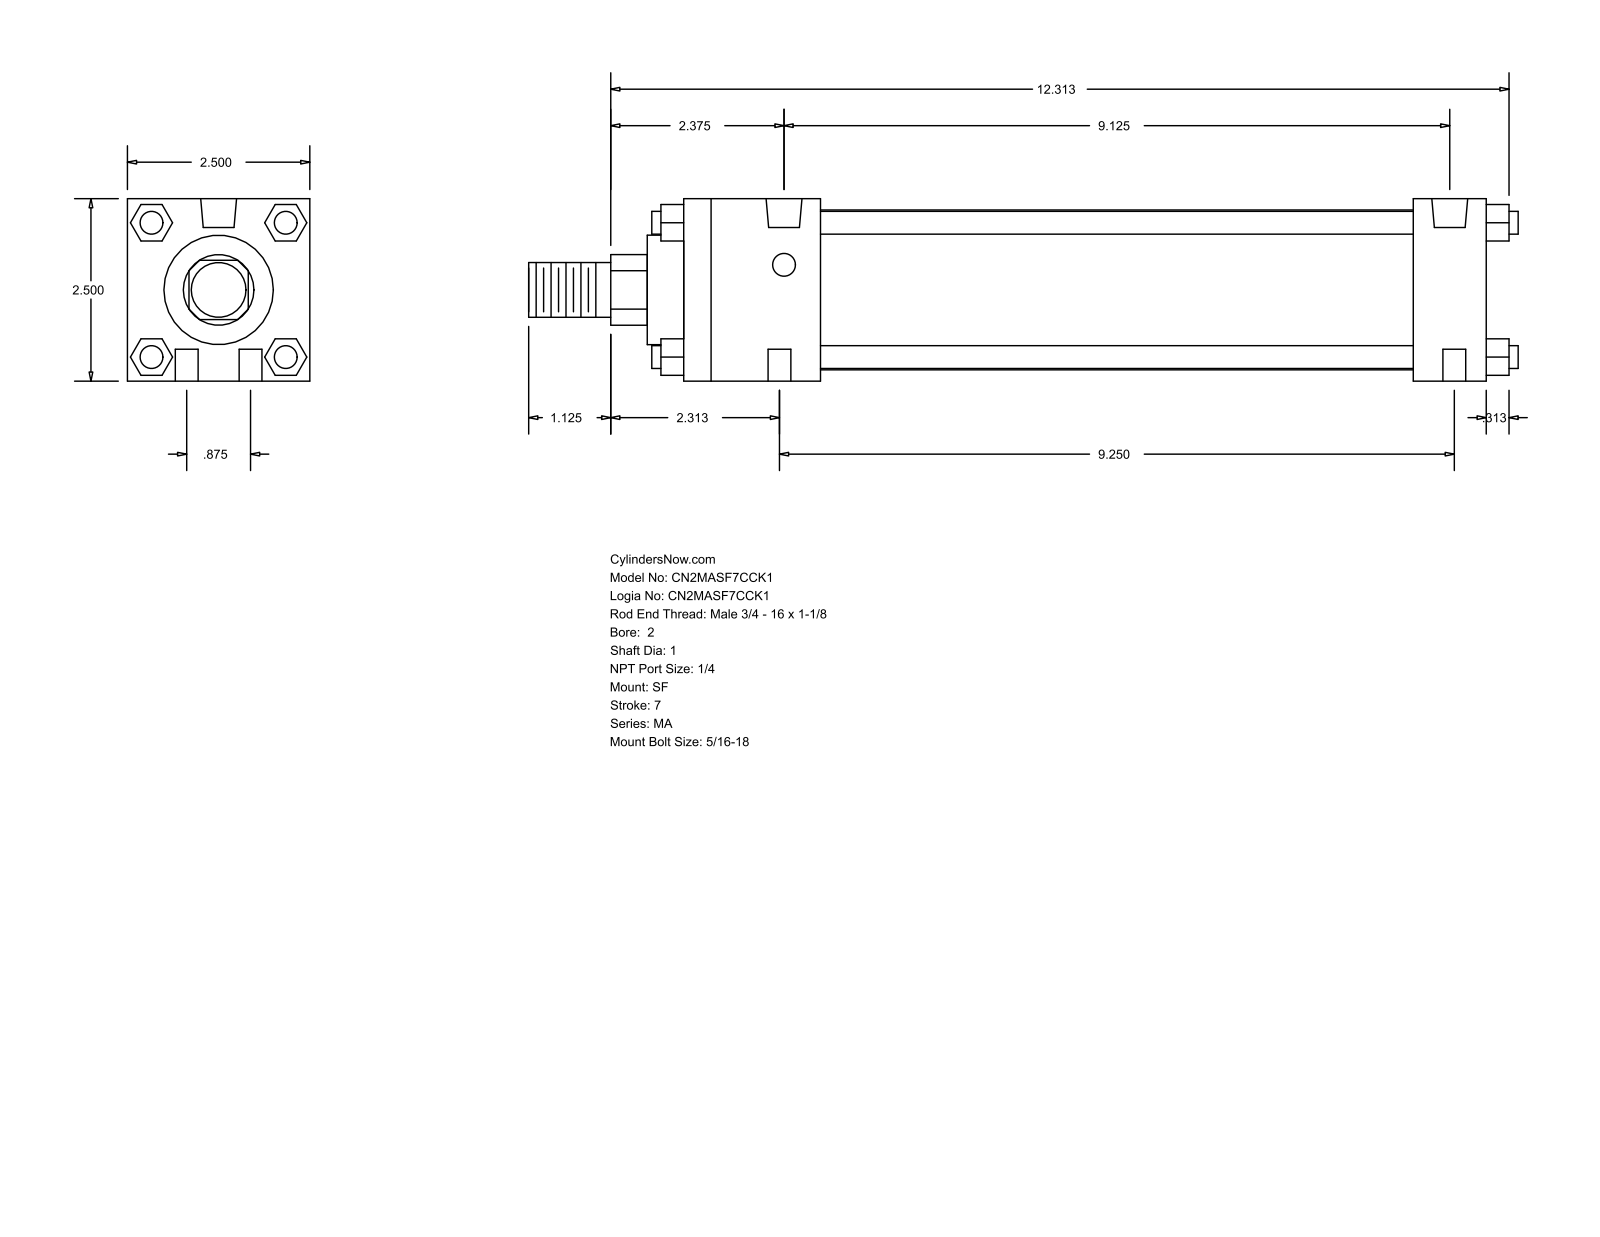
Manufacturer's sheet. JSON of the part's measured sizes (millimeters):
{"part_name": "MA_SF__0200_1", "step_written_by": "GSSL Pune (CONFIG_CONTROL_DESIGN)", "units": "millimeters", "bodies": {"solids": 0, "faces": 124, "planar": 94, "cylindrical": 30, "other": 0}, "overall_size": [344.49, 63.5, 63.5], "round_holes": [[7.94, 6], [12.49, 2]], "round_bosses_or_shafts": [[7.94, 4], [55.63, 1], [38.1, 1], [25.4, 1], [19.05, 1]], "partial_cylinders_radius": [[12.29, 1]], "face_to_face_distances": [63.5, 279.4, 12.7, 25.4, 254, 47.63, 206.37, 231.77, 40.47, 23.37], "hole_center_spacings": [11.22, 233.62, 22.22, 231.77, 234.95, 236]}
